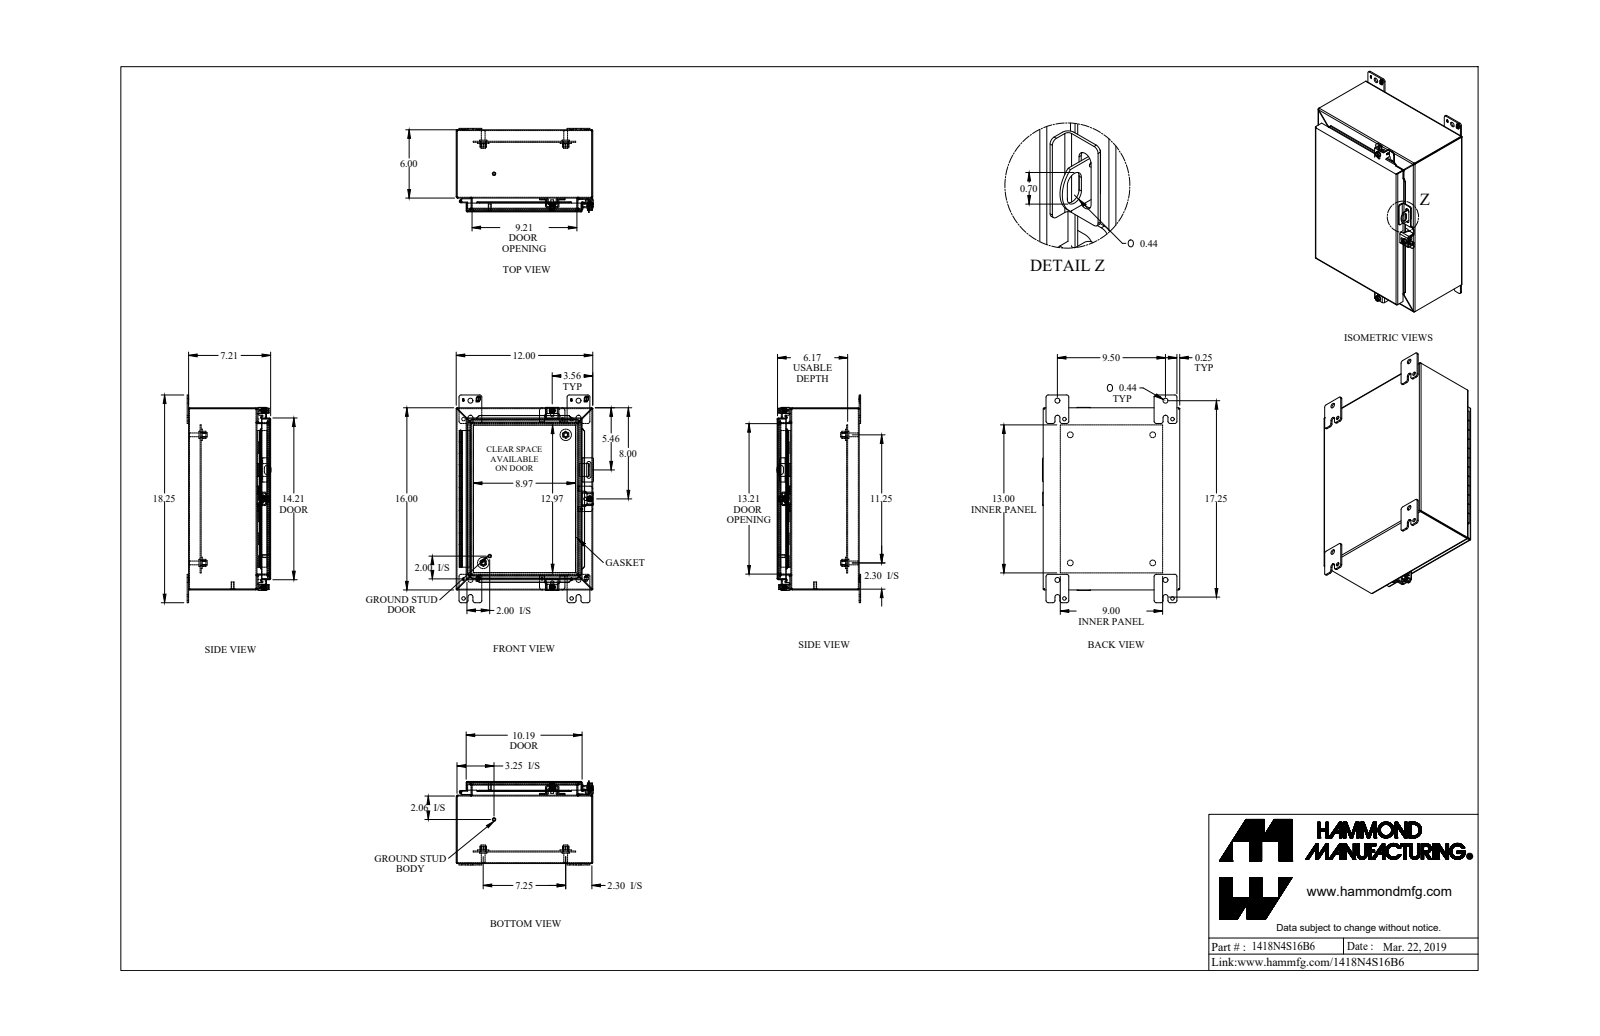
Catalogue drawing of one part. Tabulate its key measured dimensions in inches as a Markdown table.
| quantity | value |
| --- | --- |
| part name | 1418N4S16B6_Default |
| STEP written by | SolidWorks 2019 (CONFIG_CONTROL_DESIGN) |
| units | inches |
| bodies | 38 solids, 1194 faces (660 planar, 400 cylindrical, 134 other) |
| overall size | 18.25 × 12.063 × 7.375 |
| volume | 81.1 in³ |
| surface area | 2 161 in² |
| round holes (diameter × count) | 0.313 × 4, 0.437 × 4, 0.5 × 4, 0.213 × 3, 0.265 × 3, 0.375 × 3, 0.307 × 2, 0.445 × 2, 0.11 × 1, 0.125 × 1 |
| round bosses / shafts (diameter × count) | 0.65 × 4, 0.375 × 4, 0.332 × 4, 0.5 × 3, 0.39 × 3, 0.244 × 3, 1 × 2, 0.313 × 2 |
| partial cylindrical surfaces (radius × count) | 0.188 × 26, 0.036 × 24, 0.108 × 24, 0.25 × 16, 0.048 × 15, 0.143 × 15, 0.125 × 10, 0.045 × 8 |
| main face-to-face distances | 0.072, 11.928, 7.066, 7.138, 0.072, 7.138, 0.937, 7.21, 15.928, 1.009 |
| hole center spacings | 1.735, 9.5, 15.75, 18.393, 2.434, 7.25, 8.508, 11.25 |
